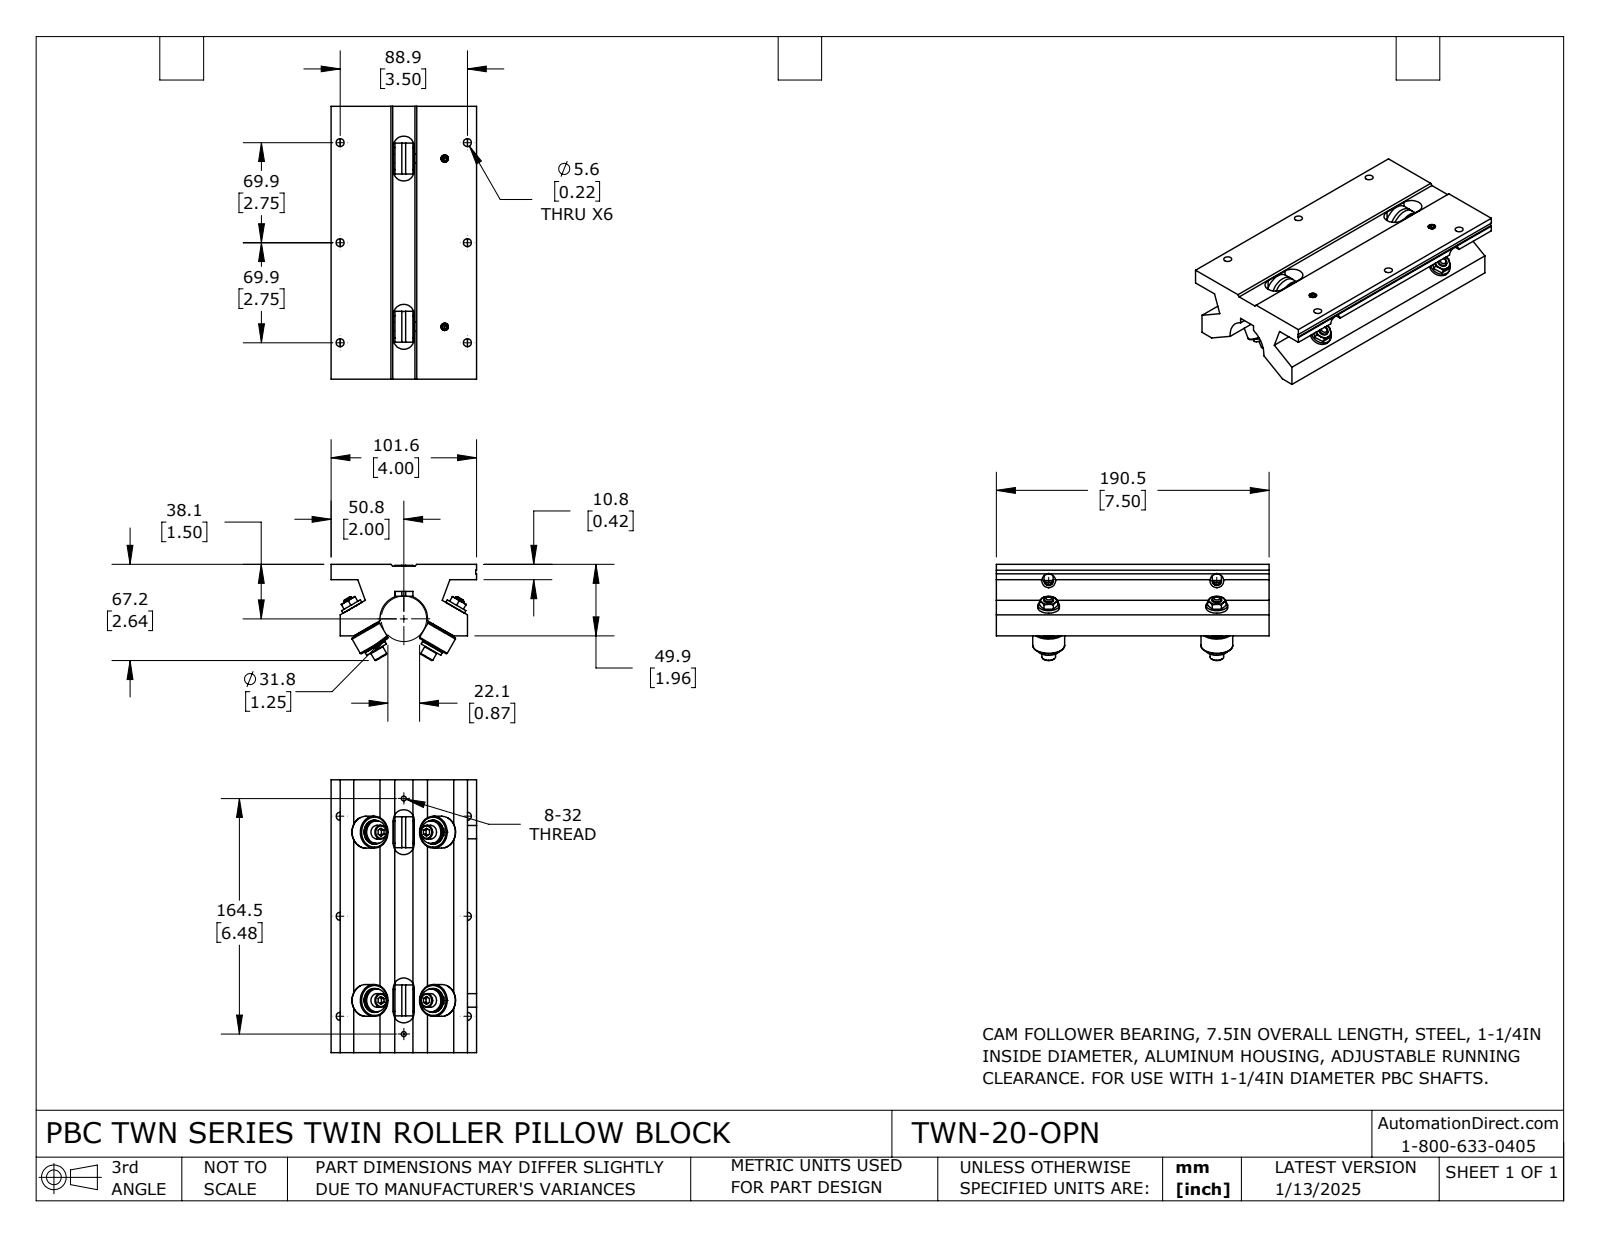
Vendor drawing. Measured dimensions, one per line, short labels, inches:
name: TWN-20-OPN
written by: SolidWorks 2023 (CONFIG_CONTROL_DESIGN)
unit: in
bodies: 27 solids, 689 faces (230 planar, 233 cylindrical, 226 other)
size: 7.5 × 4 × 2.644
volume: 34.6 in³; area: 175.7 in²
holes: 6× ⌀0.219, 4× ⌀0.185, 4× ⌀0.25, 4× ⌀0.25, 4× ⌀0.281, 4× ⌀0.287, 4× ⌀0.382, 4× ⌀0.645, 2× ⌀0.136, 2× ⌀0.201, 2× ⌀0.219, 2× ⌀0.249
bosses: 4× ⌀0.875, 4× ⌀0.625, 4× ⌀0.594, 4× ⌀0.378, 4× ⌀0.375, 4× ⌀0.25, 2× ⌀0.85, 2× ⌀0.609
rounds: 2× R0.287, 2× R0.288, 1× R0.655
face distances: 0.685, 0.424, 0.25, 1.54, 1.964, 3.75, 7.5, 3.5, 1.914, 0.374
hole spacings: 4.625, 1.817, 2.75, 3.68, 4.451, 6.238, 3.5, 0.02
